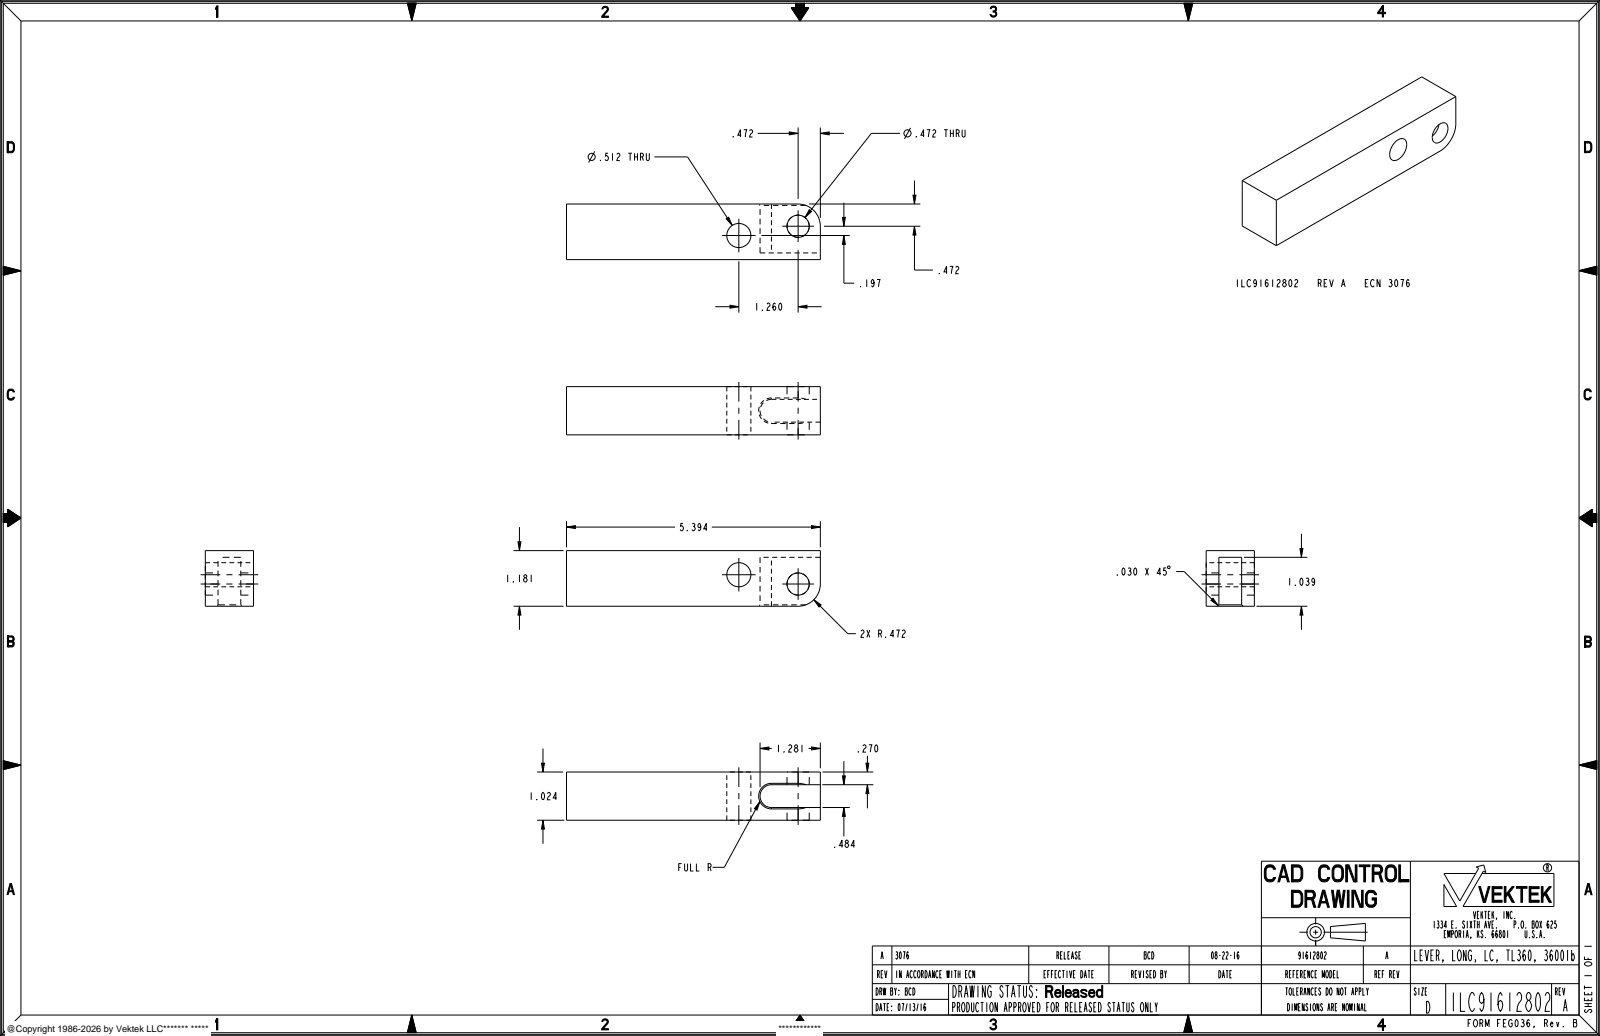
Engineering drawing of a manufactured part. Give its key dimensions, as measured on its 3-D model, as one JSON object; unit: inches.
{"part_name": "ILC91612802", "step_written_by": "PRO/ENGINEER BY PARAMETRIC TECHNOLOGY CORPORATION, 2013320 (AUTOMOTIVE_DESIGN)", "units": "inches", "bodies": {"solids": 1, "faces": 21, "planar": 11, "cylindrical": 9, "other": 1}, "overall_size": [5.394, 1.181, 1.024], "volume_in3": 5.573, "surface_area_in2": 29.65, "round_holes": [[0.472, 1], [0.512, 1]], "partial_cylinders_radius": [[0.242, 1], [0.472, 1]], "face_to_face_distances": [1.024, 1.181, 0.27, 0.754, 0.484, 1.039, 0.142, 5.394], "hole_center_spacings": [1.275]}
